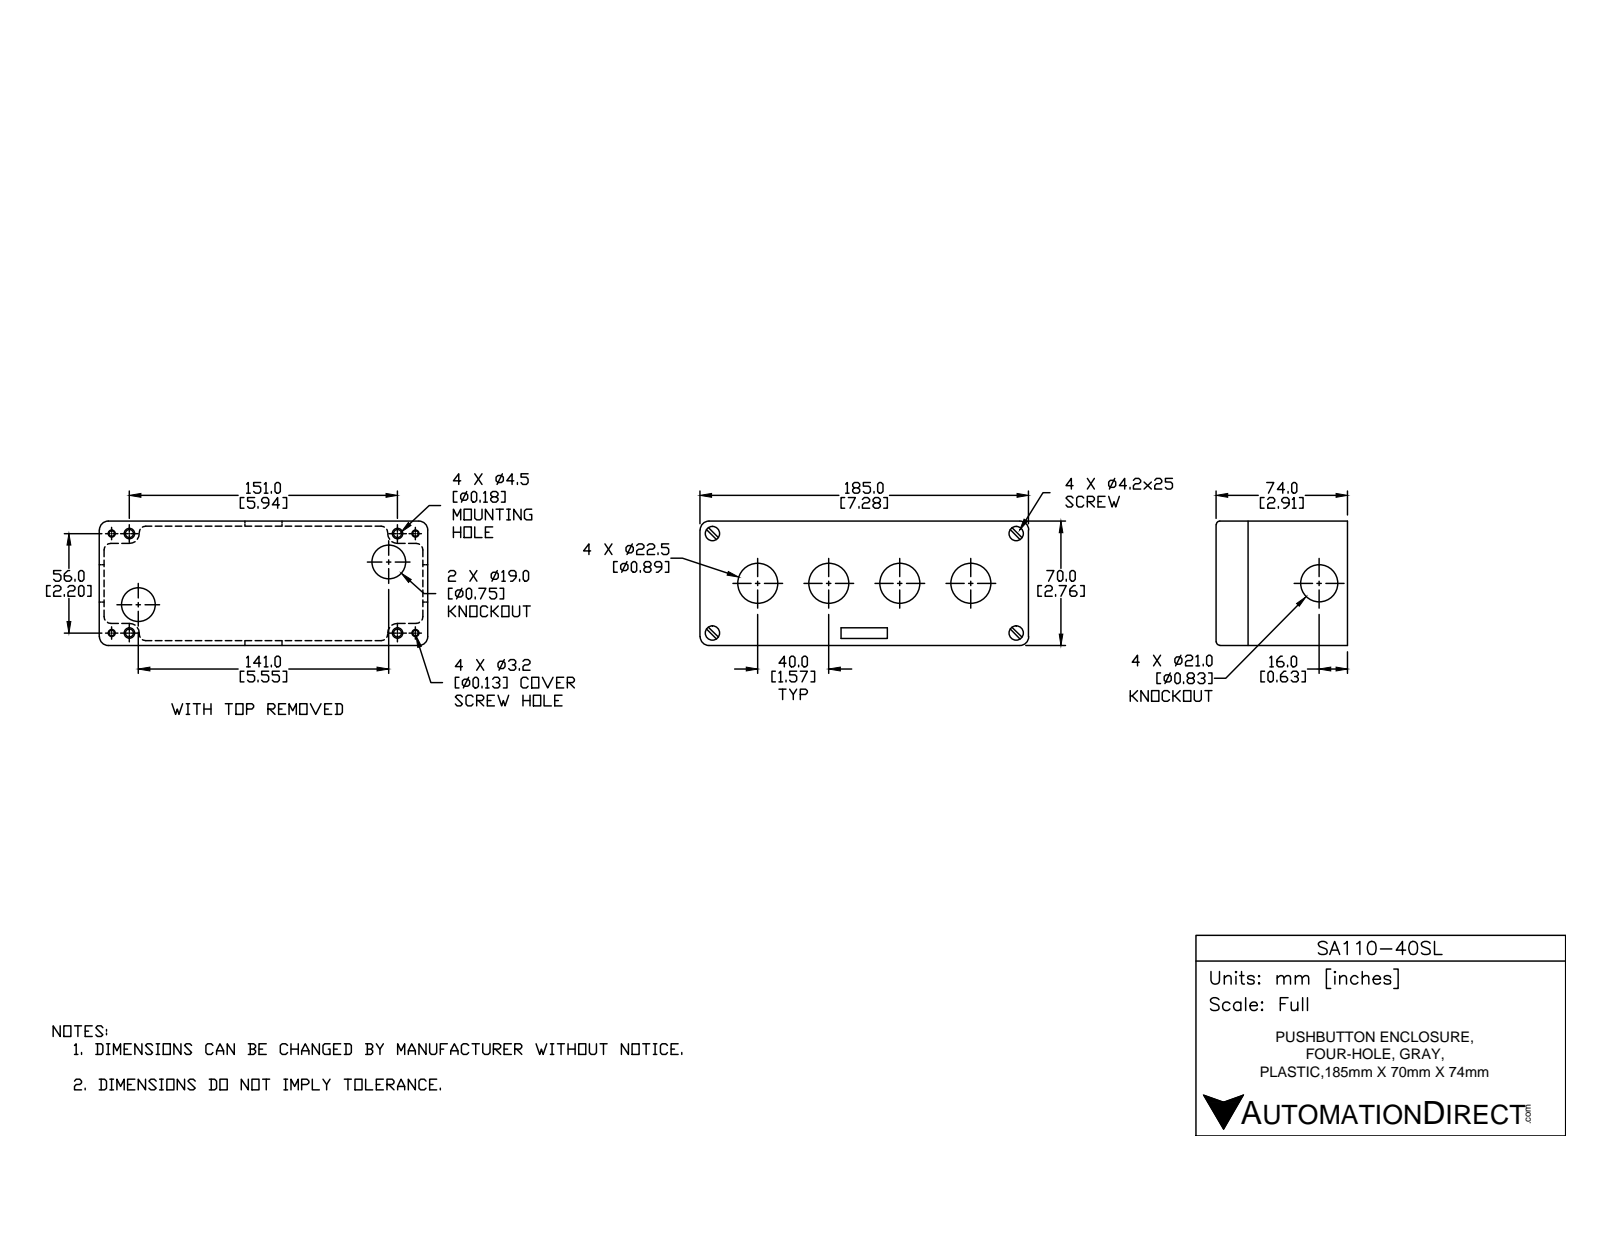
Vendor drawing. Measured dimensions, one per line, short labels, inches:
name: SA110-40SL
written by: SolidWorks 2018 (AUTOMOTIVE_DESIGN)
unit: in
bodies: 6 solids, 492 faces (132 planar, 200 cylindrical, 160 other)
size: 7.283 × 2.922 × 2.756
volume: 13.85 in³; area: 196.1 in²
holes: 4× ⌀0.126, 4× ⌀0.165, 4× ⌀0.177, 4× ⌀0.295, 4× ⌀0.315, 4× ⌀0.886, 2× ⌀0.094, 2× ⌀0.748, 2× ⌀0.827
bosses: 4× ⌀0.291, 4× ⌀0.11
rounds: 16× R0.02, 8× R0.041, 8× R0.095, 4× R0.039, 4× R0.071, 4× R0.197, 4× R0.259, 4× R0.323
face distances: 0.13, 2.626, 2.756, 0.098, 2.915, 2.817, 2.497, 2.738, 0.079, 2.837
hole spacings: 1.12, 6.339, 0.394, 1.26, 1.491, 2.205, 2.24, 2.447
